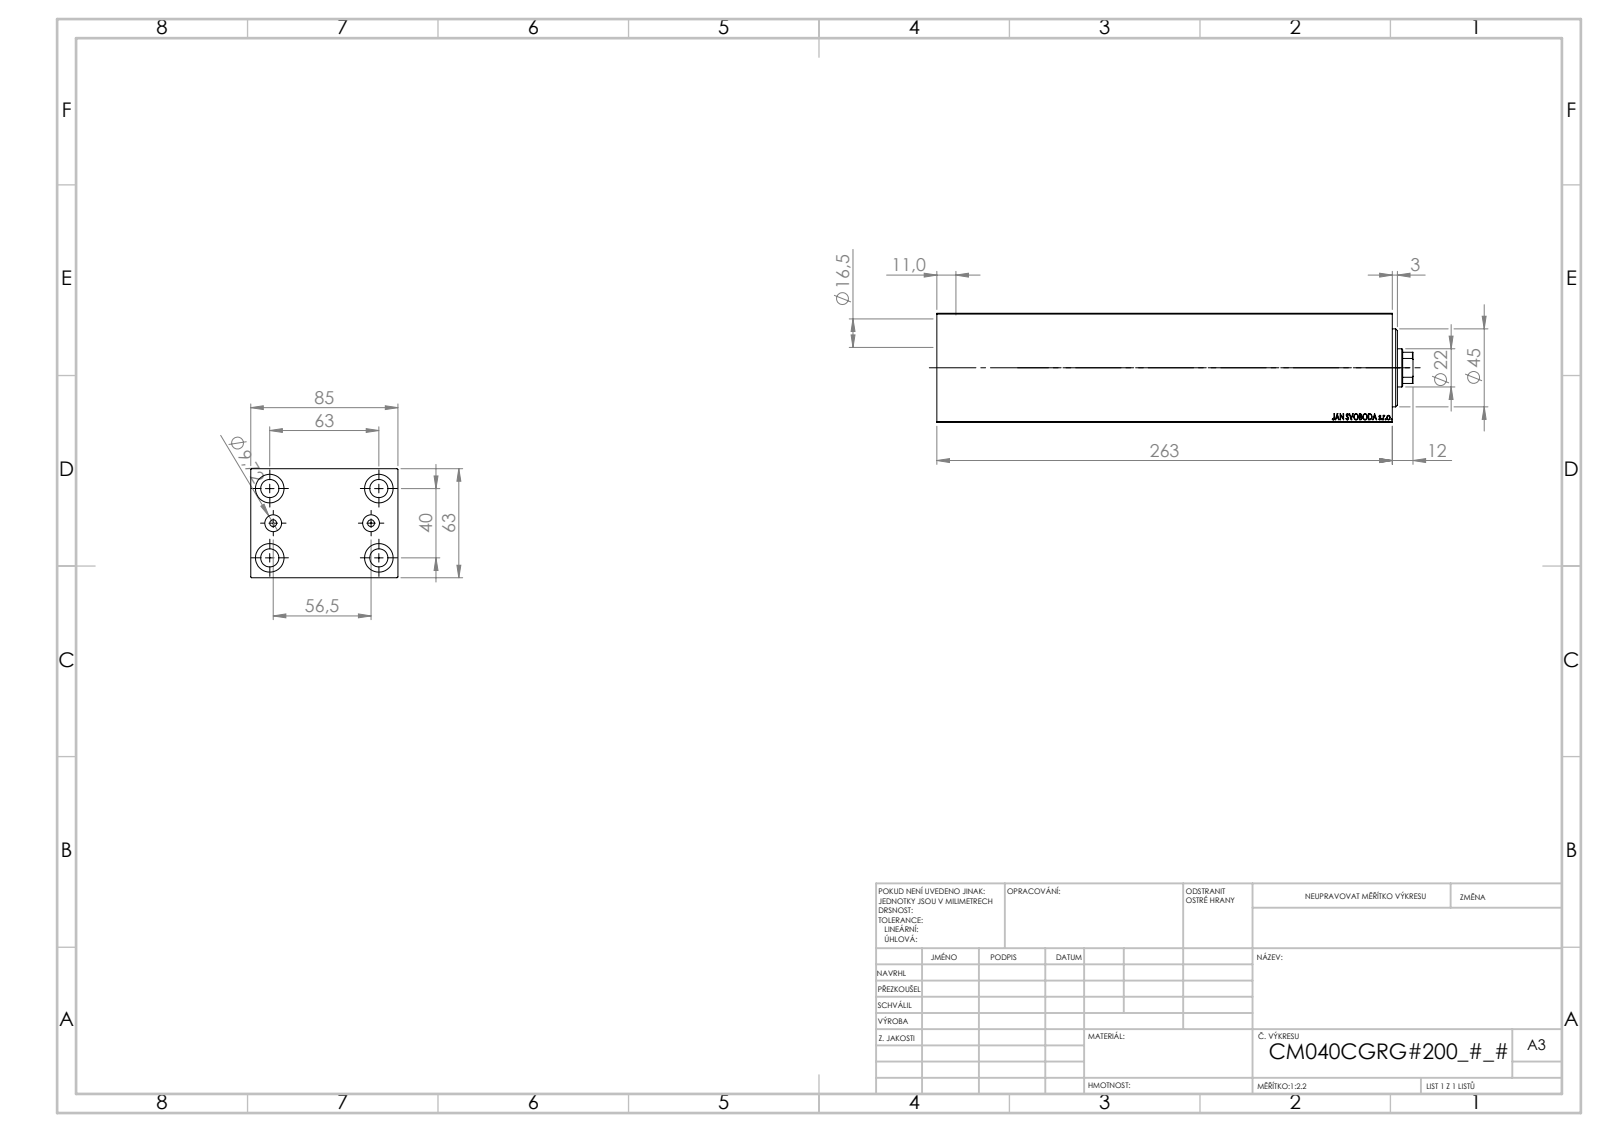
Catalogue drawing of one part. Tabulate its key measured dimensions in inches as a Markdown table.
| quantity | value |
| --- | --- |
| part name | V450CM_C_VCP; V450CM_C_Body; V450CM_VC_B |
| STEP written by | SolidWorks 2019 (CONFIG_CONTROL_DESIGN) |
| units | inches |
| bodies | 3 solids, 858 faces (408 planar, 56 cylindrical, 394 other) |
| overall size | 10.827 × 3.346 × 2.48 |
| volume | 68.83 in³ |
| surface area | 296.9 in² |
| round holes (diameter × count) | 0.413 × 4, 0.65 × 4, 0.157 × 2, 0.383 × 2, 0.492 × 1, 0.866 × 1, 1.004 × 1, 1.575 × 1, 1.654 × 1, 1.772 × 1 |
| partial cylindrical surfaces (radius × count) | 0.413 × 1 |
| main face-to-face distances | 2.48, 3.346, 0.472, 9.882, 10.354, 0.039, 9.409, 0.433, 9.921, 9.449 |
| hole center spacings | 1.469, 0.791, 0.807, 1.575, 2.434, 2.48, 2.528, 2.938 |
